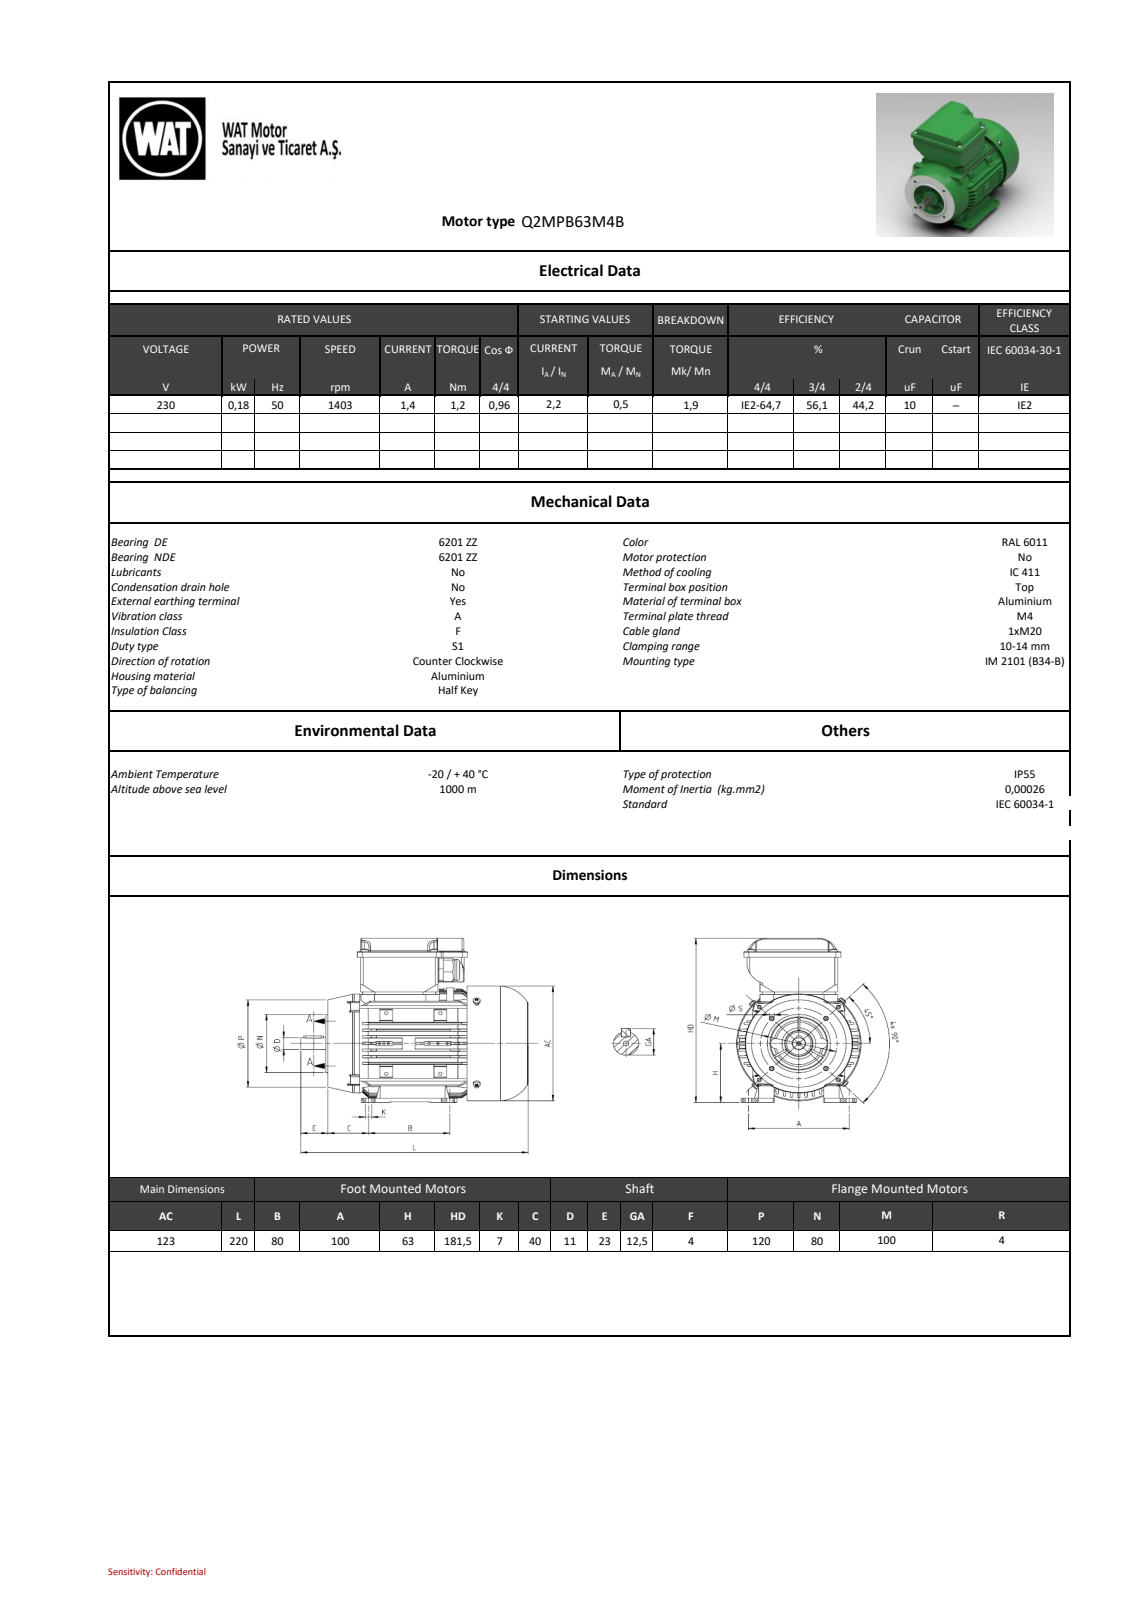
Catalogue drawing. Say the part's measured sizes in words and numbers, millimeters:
The part is named "BY6434017xx_004-TK_QM63-80; BY6424130xx_004-TKK_QM63-80; BY6424189xx_005-MOTOR_KAPAGI_QS63FB_ISLEME; BY6423003xx_006-FAN_KAPAGI_QS63 (+8 more)". Its 3-D file was written by "SIEMENS PLM Software NX2206.8101 (AUTOMOTIVE_DESIGN)". It is 36 solids with 2421 faces: 1201 planar, 834 cylindrical and 386 other. Overall it measures 219.47 by 181.5 by 123 millimeters. Its volume is 643 347 cubic millimeters and its surface area 427 999 square millimeters. Round holes: 10 of diameter 3.65, 8 of diameter 4.5, 6 of diameter 2.5, 5 of diameter 3.3, 4 of diameter 3.5, 4 of diameter 4, 4 of diameter 4.2, 4 of diameter 4.65, 4 of diameter 4.8, 4 of diameter 6, 3 of diameter 3, 2 of diameter 7. Round bosses or shafts: 8 of diameter 8, 8 of diameter 4, 8 of diameter 3, 1 of diameter 123, 1 of diameter 120, 1 of diameter 80, 1 of diameter 70, 1 of diameter 30. Partial cylindrical surfaces (rounded edges, fillets, slot ends): 212 of radius 0.5, 136 of radius 1, 81 of radius 2, 21 of radius 3, 20 of radius 2.5, 10 of radius 5, 9 of radius 5.5, 8 of radius 1.5. The main face-to-face distances are 3, 7.02, 27.96, 4, 1, 4.5, 10.5, 1.5, 7, 28.05. The hole center spacings are 55, 54, 54.45, 77, 0.61, 62.8, 63, 66.91.
